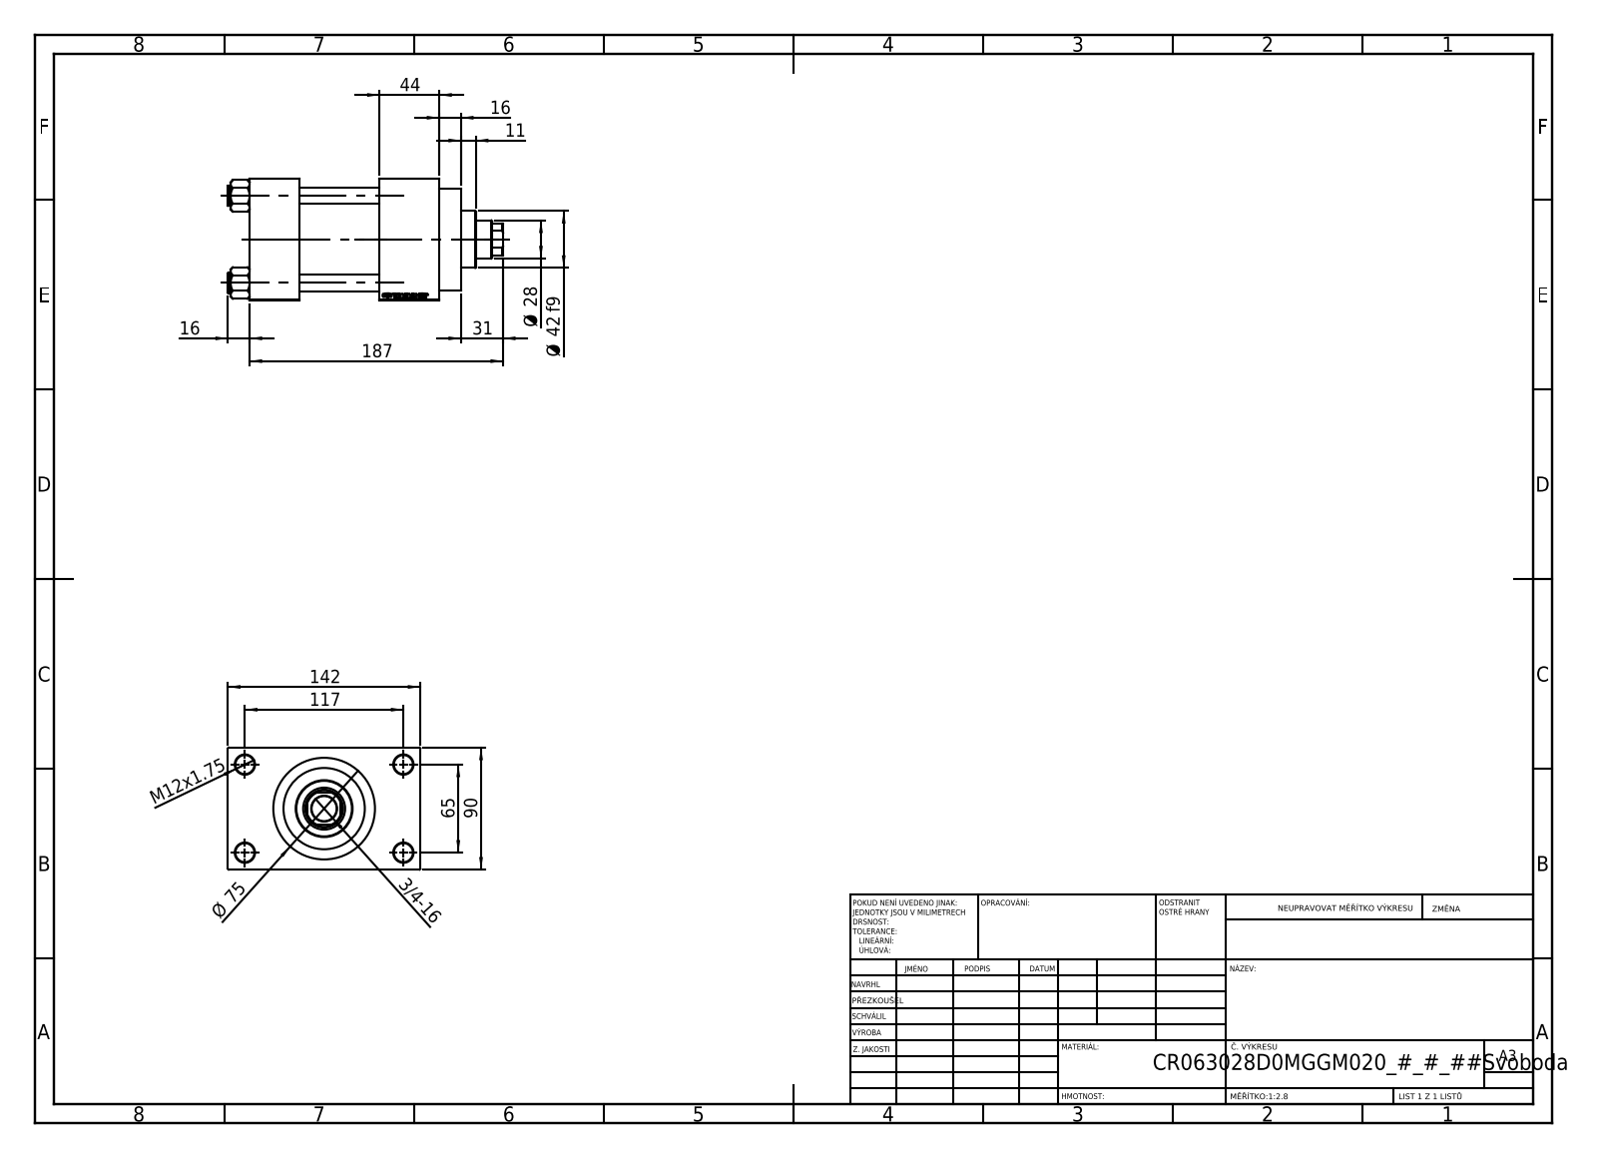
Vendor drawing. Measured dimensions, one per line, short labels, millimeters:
name: V215CR_VCP_D; NUT_M5_D; V215CR_D_Body; V215_VC_A (+1 more)
written by: SolidWorks 2019 (CONFIG_CONTROL_DESIGN)
unit: mm
bodies: 11 solids, 1104 faces (497 planar, 89 cylindrical, 518 other)
size: 203 × 142 × 90
volume: 1 105 000 mm³; area: 198 607 mm²
holes: 4× ⌀12, 4× ⌀14, 2× ⌀7, 2× ⌀20.96, 2× ⌀30, 1× ⌀18.5, 1× ⌀28, 1× ⌀31, 1× ⌀50, 1× ⌀60, 1× ⌀63
bosses: 4× ⌀15, 1× ⌀75, 1× ⌀69, 1× ⌀42
rounds: 1× R13.5
face distances: 90, 59, 37, 96, 140, 103, 44, 26, 116, 142
hole spacings: 26.35, 45.47, 64.3, 66.92, 69.81, 90.65, 111.34, 65
